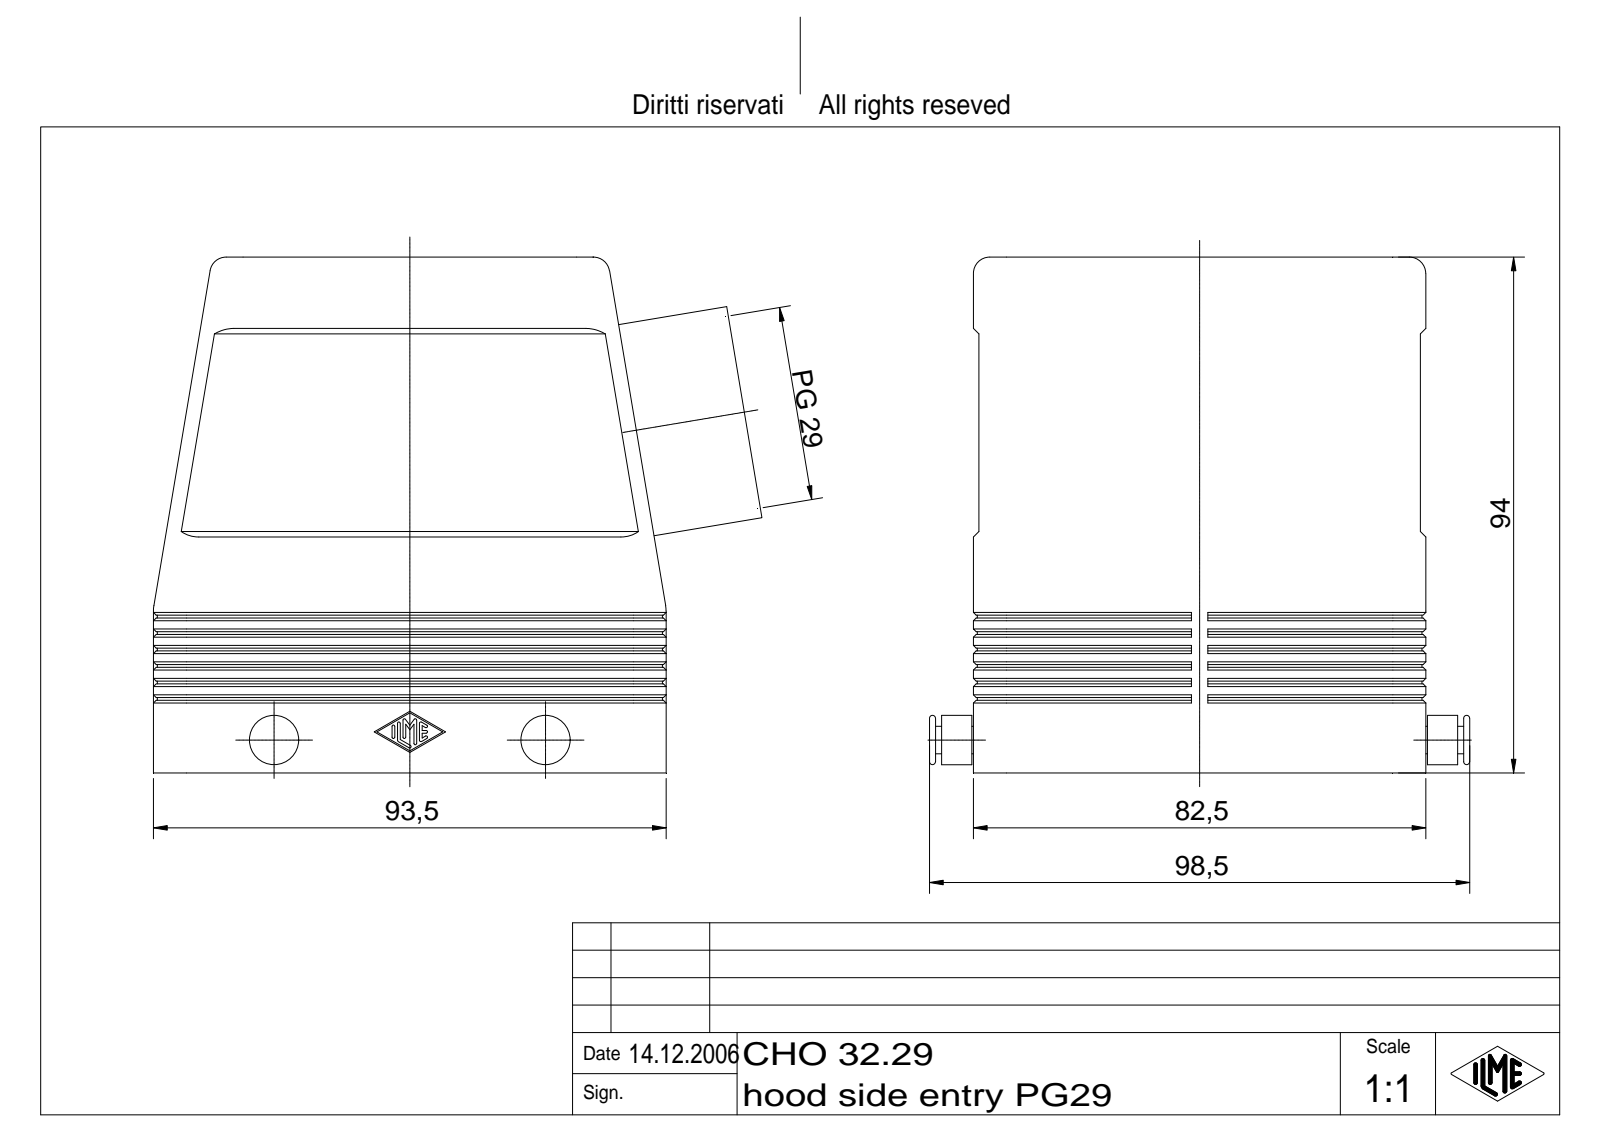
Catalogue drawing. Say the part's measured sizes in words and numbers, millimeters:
The part is named "CHO 32.29". Its 3-D file was written by "Autodesk Inventor 7 (AUTOMOTIVE_DESIGN)". It is 1 solid with 613 faces: 207 planar, 158 cylindrical and 248 other. Overall it measures 110.96 by 98.5 by 94 millimeters. Its volume is 148 907 cubic millimeters and its surface area 79 463 square millimeters. Round holes: 4 of diameter 2.46, 4 of diameter 3.5, 1 of diameter 33.48, 1 of diameter 35.48. Round bosses or shafts: 2 of diameter 9, 2 of diameter 5, 1 of diameter 39. Partial cylindrical surfaces (rounded edges, fillets, slot ends): 14 of radius 0.25, 12 of radius 2, 10 of radius 6, 4 of radius 3, 2 of radius 5.3. The main face-to-face distances are 4, 78.5, 74.5, 82.5, 3, 11, 71.5, 1, 77.5, 81.5. The hole center spacings are 27, 77.5, 82.07.
